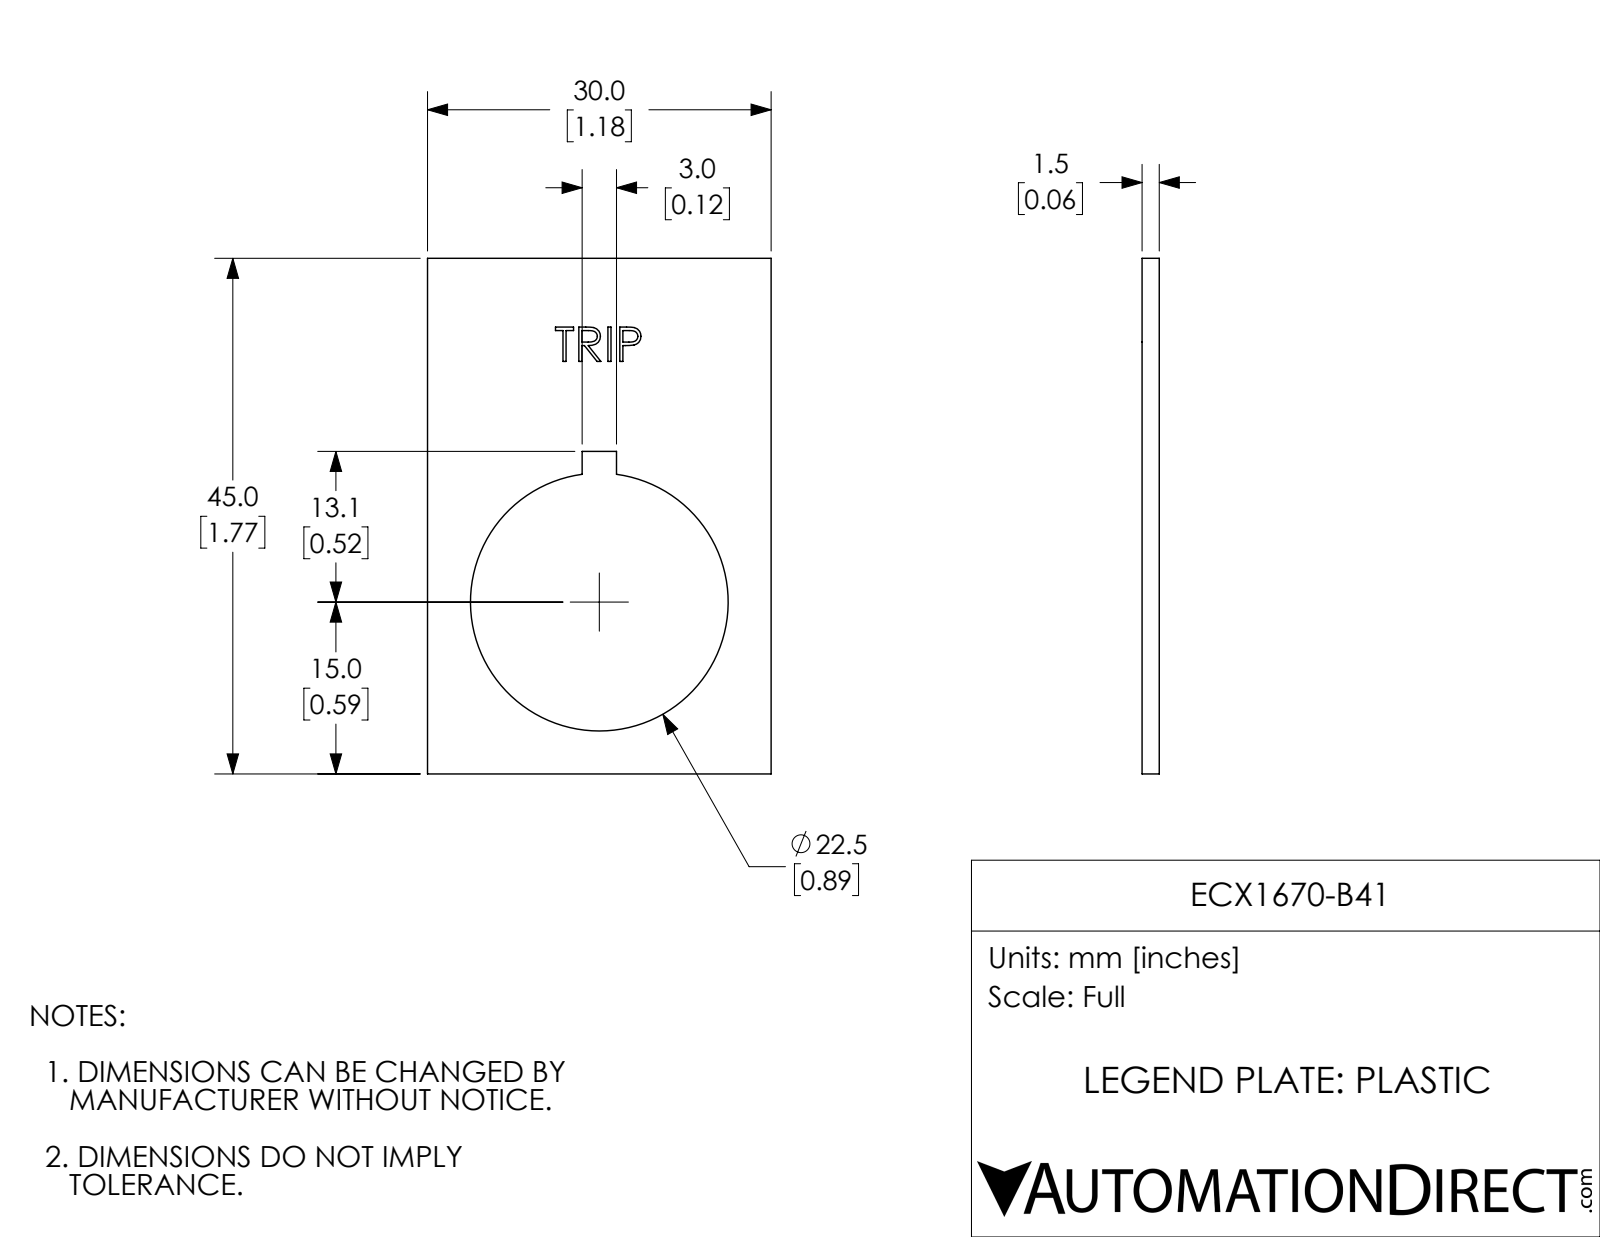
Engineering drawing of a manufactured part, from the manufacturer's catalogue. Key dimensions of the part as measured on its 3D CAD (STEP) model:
Part name (STEP PRODUCT): ECX1670-B41
STEP written by: SolidWorks 2017 (AUTOMOTIVE_DESIGN)
Units: inches
Bodies: 1 solid, 60 faces (46 planar, 3 cylindrical, 11 other)
Overall size (bounding box): 1.772 × 1.181 × 0.059
Volume: 0.087 in³ · Surface area: 3.459 in²
Round holes (diameter × count): ⌀0.886 ×1
Main face-to-face distances: 0.059, 1.181, 1.772, 0.058, 0.531, 0.65, 1.108, 0.663, 0.118, 0.52
